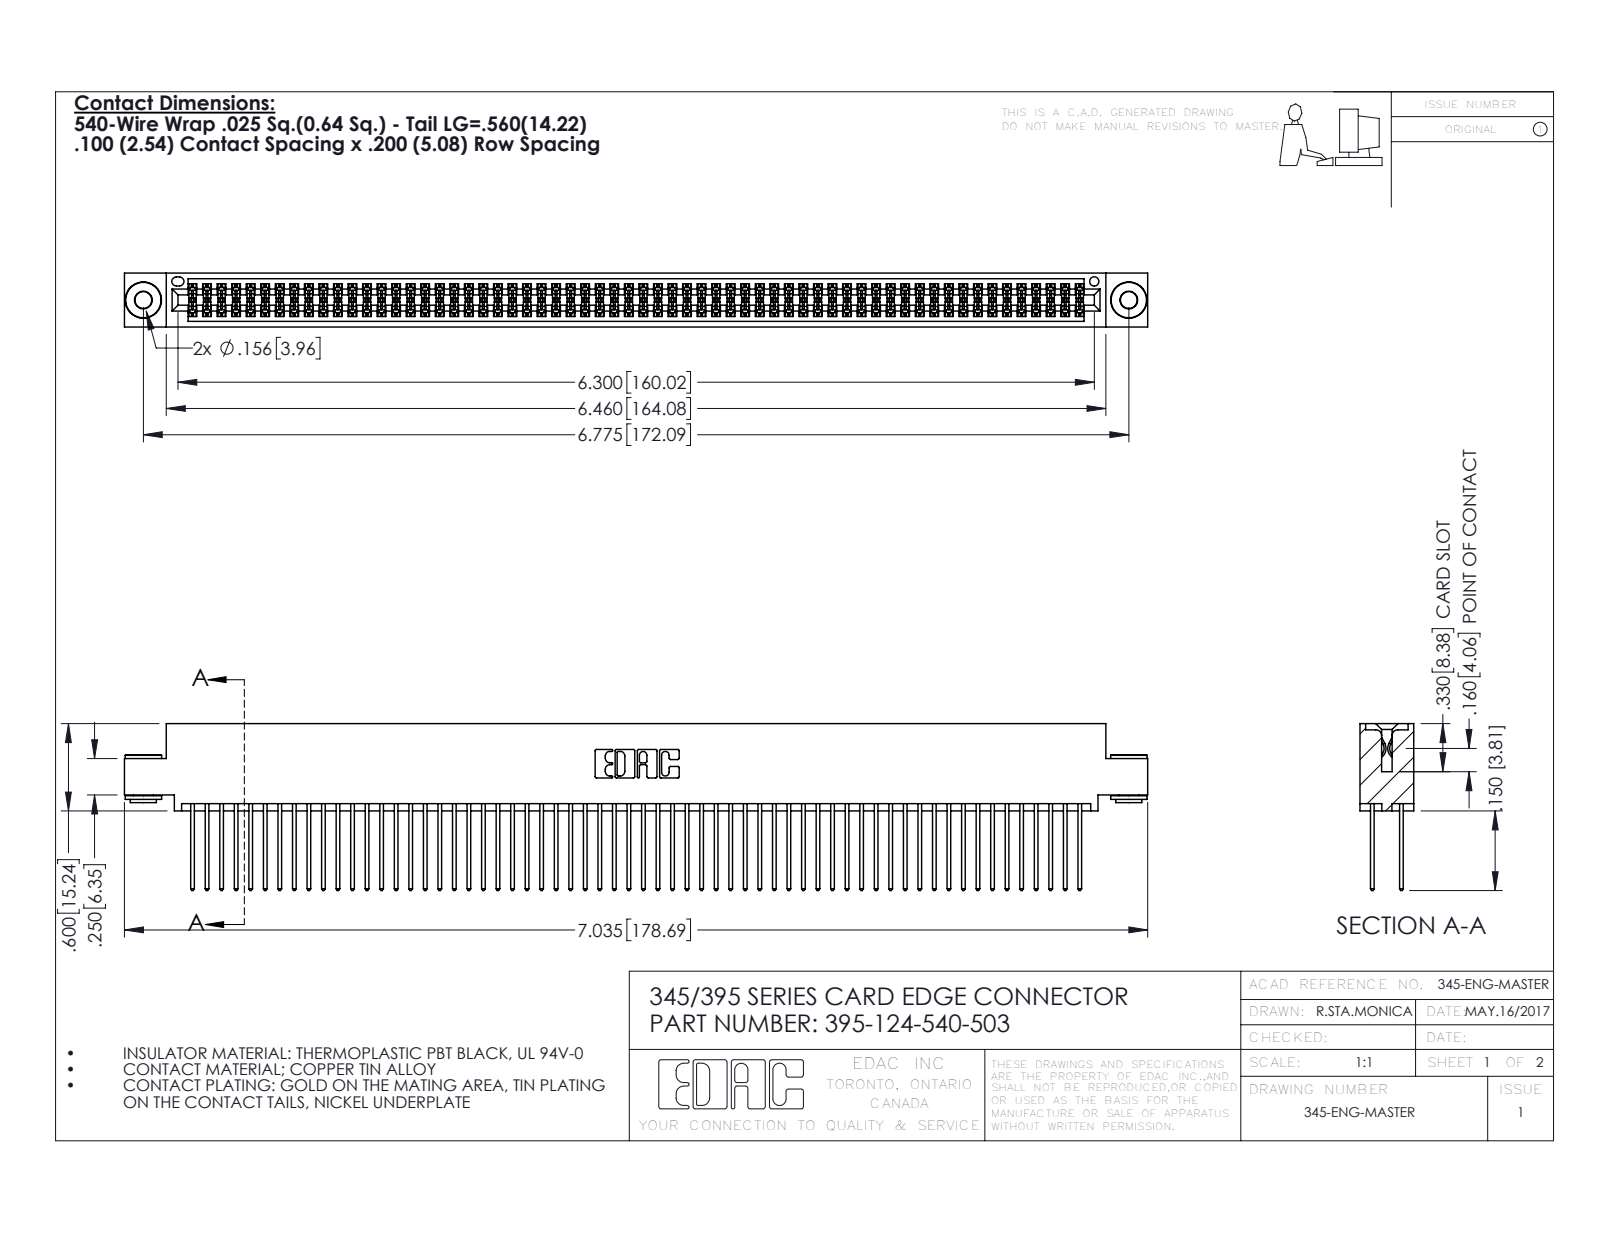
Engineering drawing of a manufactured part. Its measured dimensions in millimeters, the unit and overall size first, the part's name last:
Units: millimetres
Overall size (bounding box): 178.7 × 29.1 × 9.4
Round holes (diameter × count): ⌀2.9 ×2, ⌀4 ×2, ⌀1.6 ×1
Round bosses / shafts (diameter × count): ⌀6.4 ×2, ⌀4.6 ×2, ⌀3.5 ×2
Partial cylindrical surfaces — rounded edges, fillets, slot ends (radius × count): R0.2 ×186, R0.3 ×124, R0.3 ×22, R0.2 ×6, R0.8 ×6, R0.7 ×3, R0.4 ×2, R0.5 ×2
Main face-to-face distances: 1.8, 7.6, 5.1, 0.6, 2.5, 6.9, 5.7, 9.4, 4.4, 3.8
Hole centre spacings: 6.9, 166.1, 172.1
Volume: 17 960 mm³ · Surface area: 29 410 mm²
Bodies: 127 solids, 6368 faces (4186 planar, 2174 cylindrical, 8 other)
Part name (STEP PRODUCT): 345-292-001_345-293-140; 345-250-002_345-250-002-102; 345 Part_0.110 Offset - 0.156 Dia-TH; 395-124-540-503
STEP written by: SolidWorks 2016 (CONFIG_CONTROL_DESIGN)
